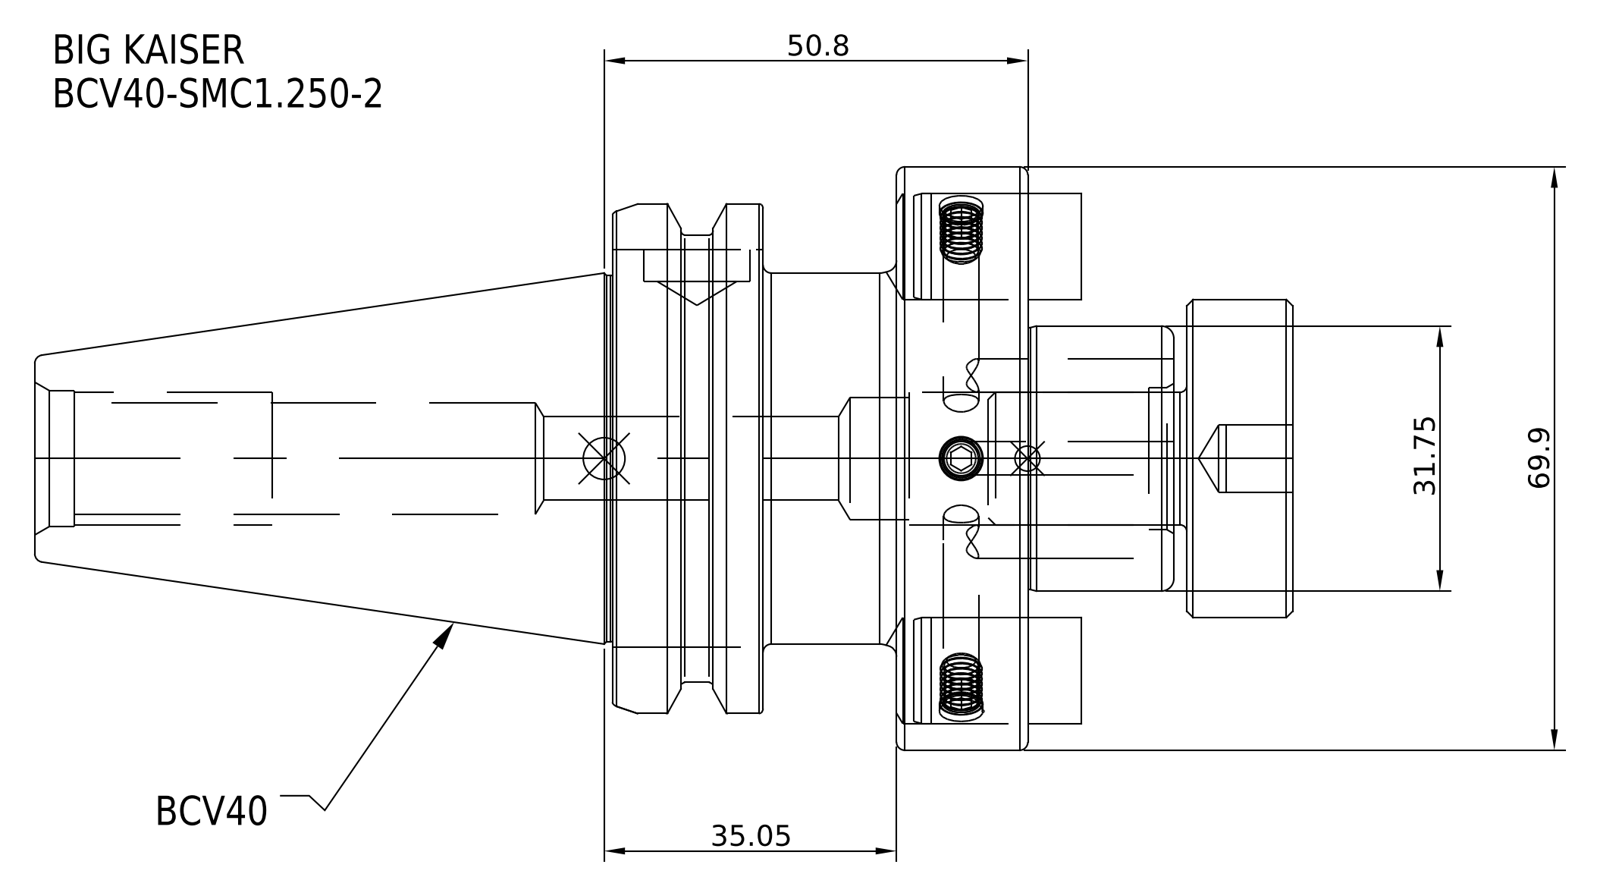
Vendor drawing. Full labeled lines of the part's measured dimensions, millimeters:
Part name (STEP PRODUCT): BCV40-SMC1_250-2
STEP written by: SolidWorks 2021 (CONFIG_CONTROL_DESIGN)
Units: millimetres
Bodies: 1 solid, 38 faces (18 planar, 14 cylindrical, 6 other)
Overall size (bounding box): 125.45 × 69.9 × 69.9
Volume: 205 496 mm³ · Surface area: 28 895 mm²
Round holes (diameter × count): ⌀14.68 ×1
Round bosses / shafts (diameter × count): ⌀69.9 ×1, ⌀63.5 ×1, ⌀56.36 ×1, ⌀44.45 ×1
Main face-to-face distances: 15.75, 49.8, 34.05, 31.75, 16, 18.05, 119.05, 103.3, 87.3, 69.25
